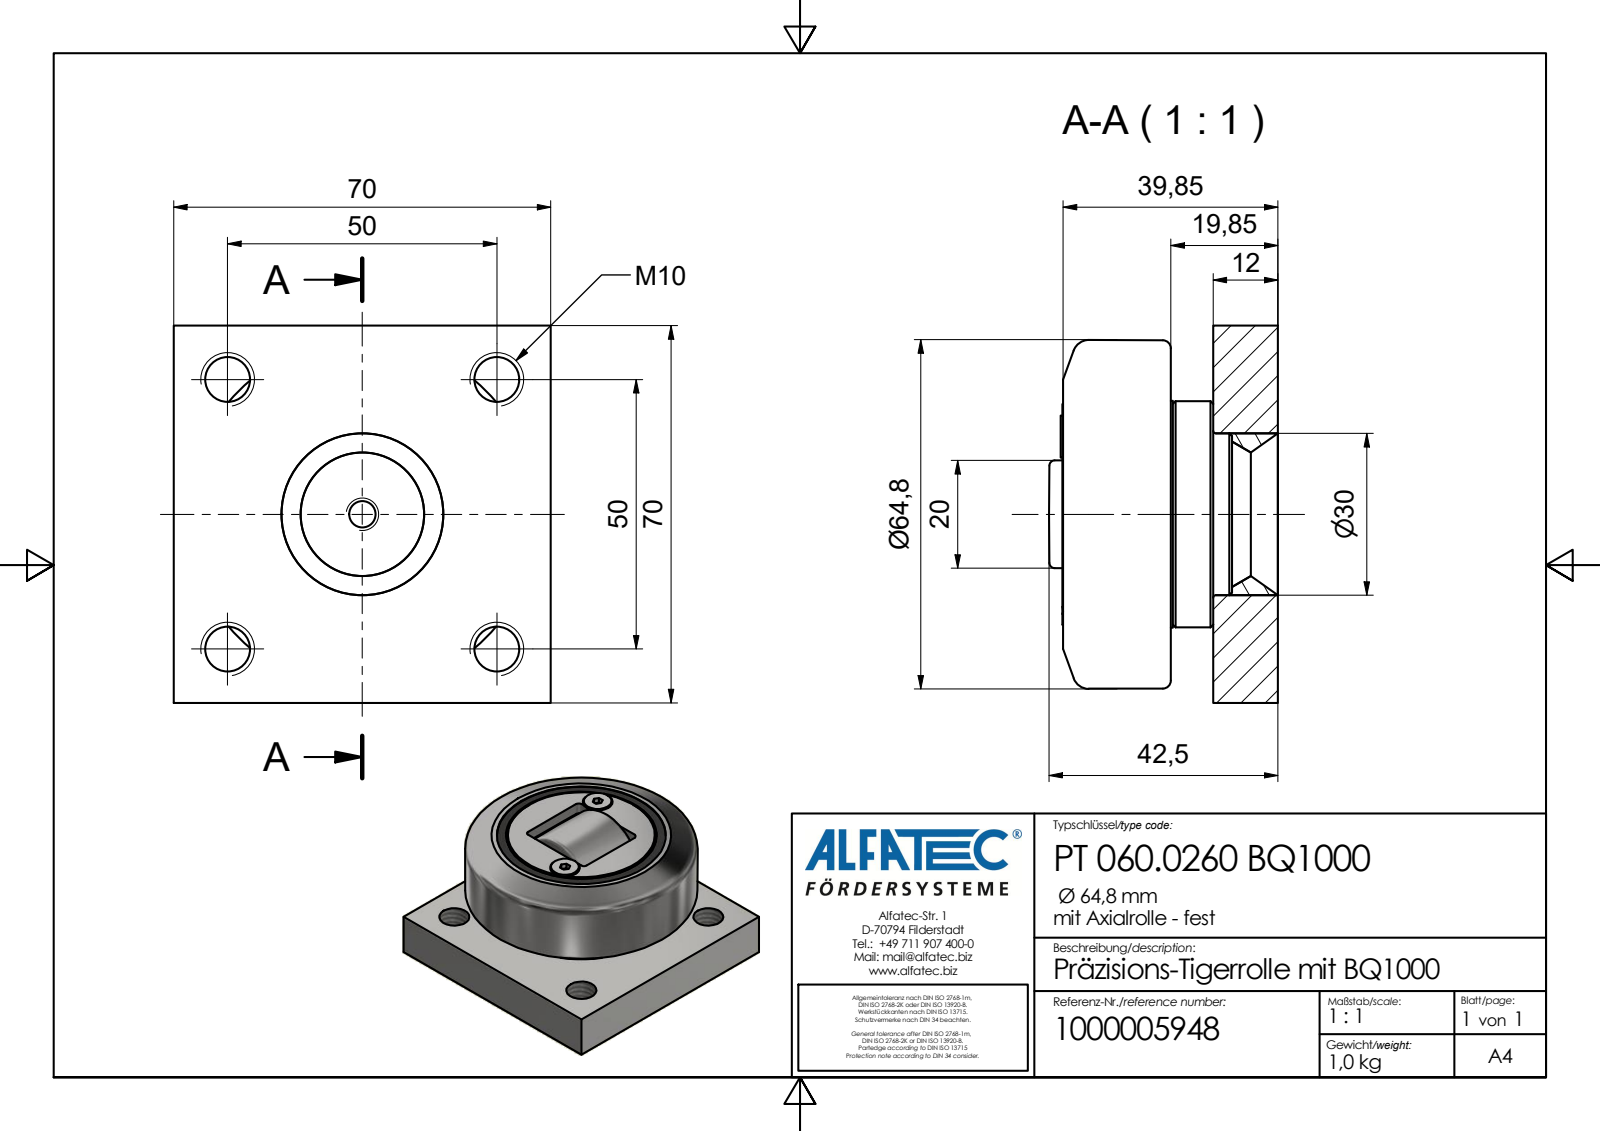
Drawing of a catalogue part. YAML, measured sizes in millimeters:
part_name: "PT 060.0260 BQ1000_Kontur"
step_written_by: "Autodesk Inventor 2020 (AP242_MANAGED_MODEL_BASED_3D_ENGINEERING_MIM_LF)"
units: millimeters
bodies: {solids: 1, faces: 439, planar: 244, cylindrical: 167, other: 28}
overall_size: [70, 70, 42.5]
volume: 123132
surface_area: 45321
round_holes:
  - {diameter: 8.38, count: 4}
  - {diameter: 2.5, count: 2}
  - {diameter: 4.3, count: 2}
  - {diameter: 2, count: 1}
  - {diameter: 3, count: 1}
  - {diameter: 4.92, count: 1}
  - {diameter: 14.4, count: 1}
  - {diameter: 15, count: 1}
  - {diameter: 38, count: 1}
  - {diameter: 42, count: 1}
  - {diameter: 42.97, count: 1}
  - {diameter: 47, count: 1}
round_bosses_or_shafts:
  - {diameter: 4, count: 38}
  - {diameter: 2, count: 20}
  - {diameter: 7.8, count: 2}
  - {diameter: 45.5, count: 1}
  - {diameter: 45, count: 1}
  - {diameter: 42.1, count: 1}
  - {diameter: 41.5, count: 1}
  - {diameter: 37, count: 1}
partial_cylinders:
  - {radius: 1, count: 8}
  - {radius: 1.35, count: 2}
  - {radius: 1.5, count: 1}
  - {radius: 14, count: 1}
face_to_face_distances: [12, 70, 19.85, 7.85, 3.35, 0.75, 28, 20, 40, 20.15]
hole_center_spacings: [35.36, 50, 16.5, 20.02, 34.65, 42.94, 51.42, 70.71]
